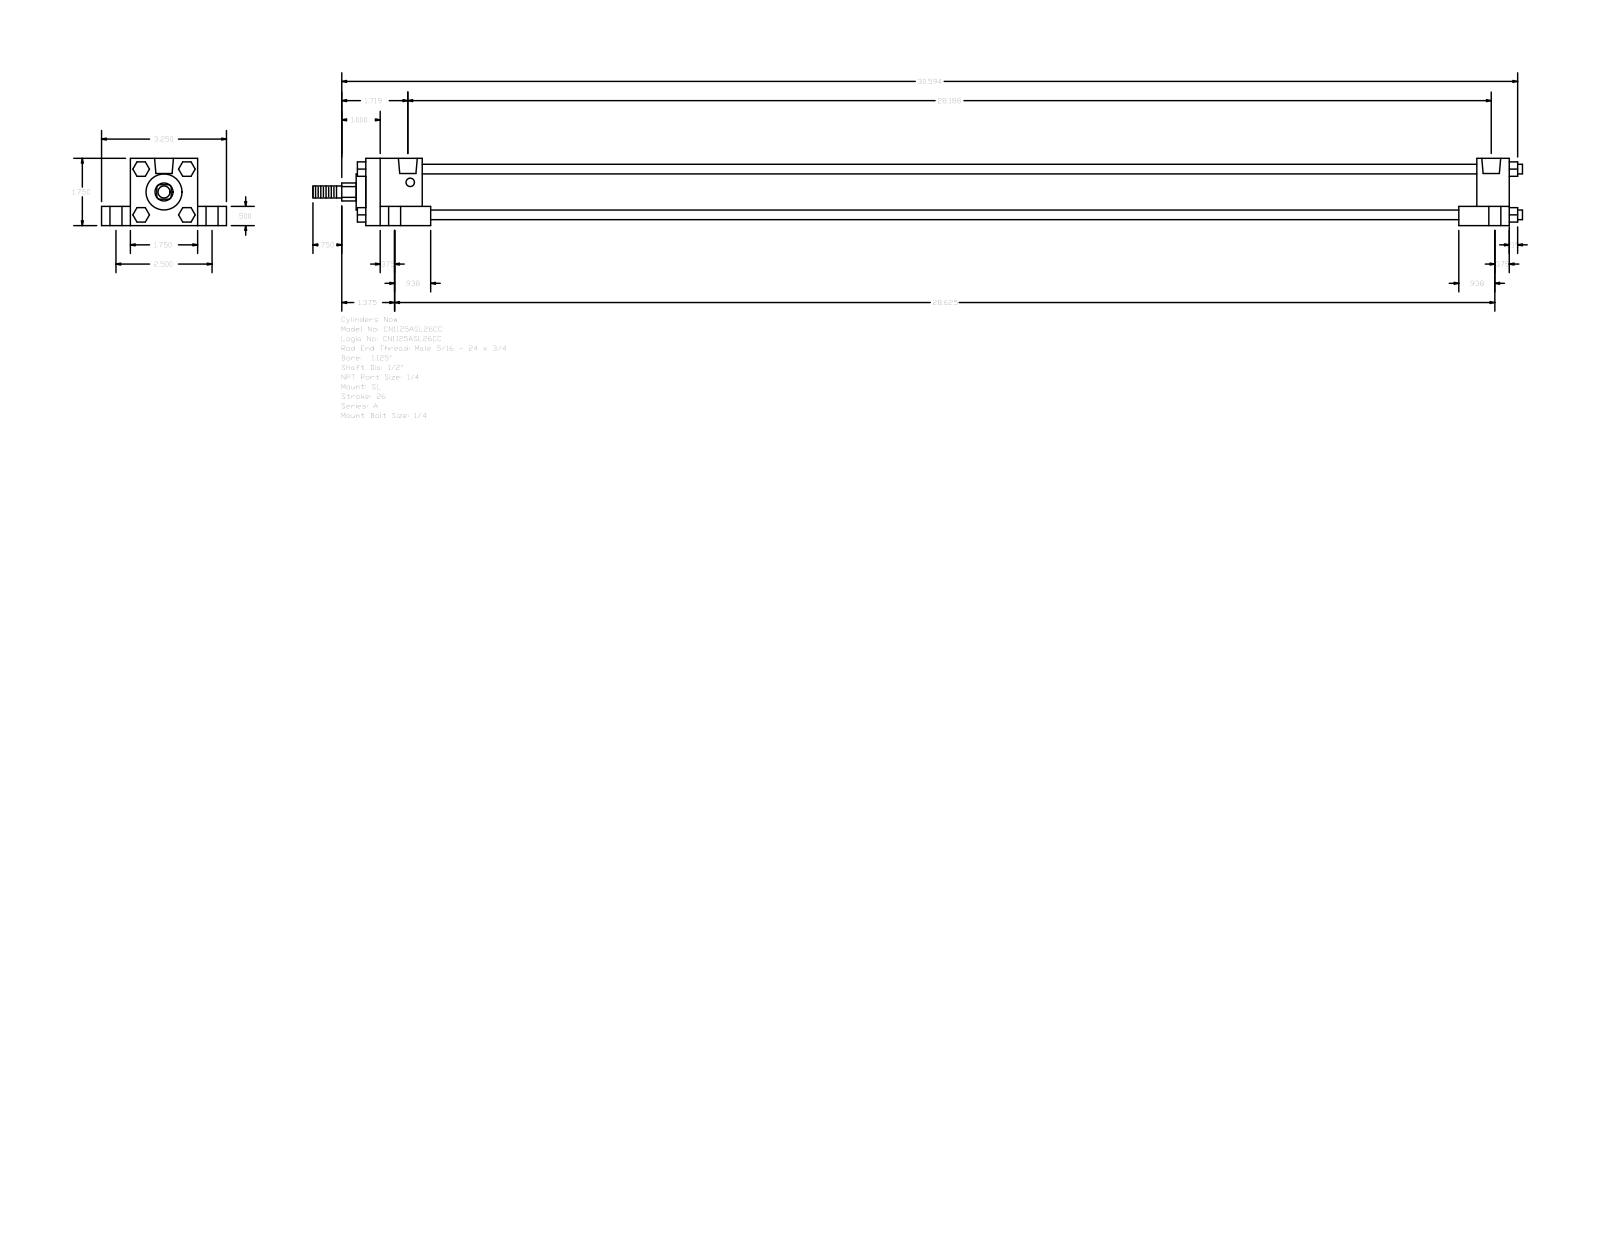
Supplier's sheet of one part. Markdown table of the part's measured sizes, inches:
| quantity | value |
| --- | --- |
| part name | A_SL__0112_0.5 |
| STEP written by | GSSL Pune (CONFIG_CONTROL_DESIGN) |
| units | inches |
| bodies | 0 solids, 150 faces (114 planar, 36 cylindrical, 0 other) |
| overall size | 31.469 × 3.25 × 1.75 |
| round holes (diameter × count) | 0.219 × 4, 0.313 × 4, 0.563 × 4, 0.492 × 2 |
| round bosses / shafts (diameter × count) | 0.25 × 4, 1.255 × 1, 0.937 × 1, 0.5 × 1, 0.313 × 1 |
| partial cylindrical surfaces (radius × count) | 0.234 × 1 |
| main face-to-face distances | 1.75, 1.25, 0.5, 0.75, 2.5, 28.281, 29.75, 28.906, 0.844, 1.469 |
| hole center spacings | 1.254, 1.26, 1.296, 1.315, 2.5, 28.063, 28.246, 28.309 |
